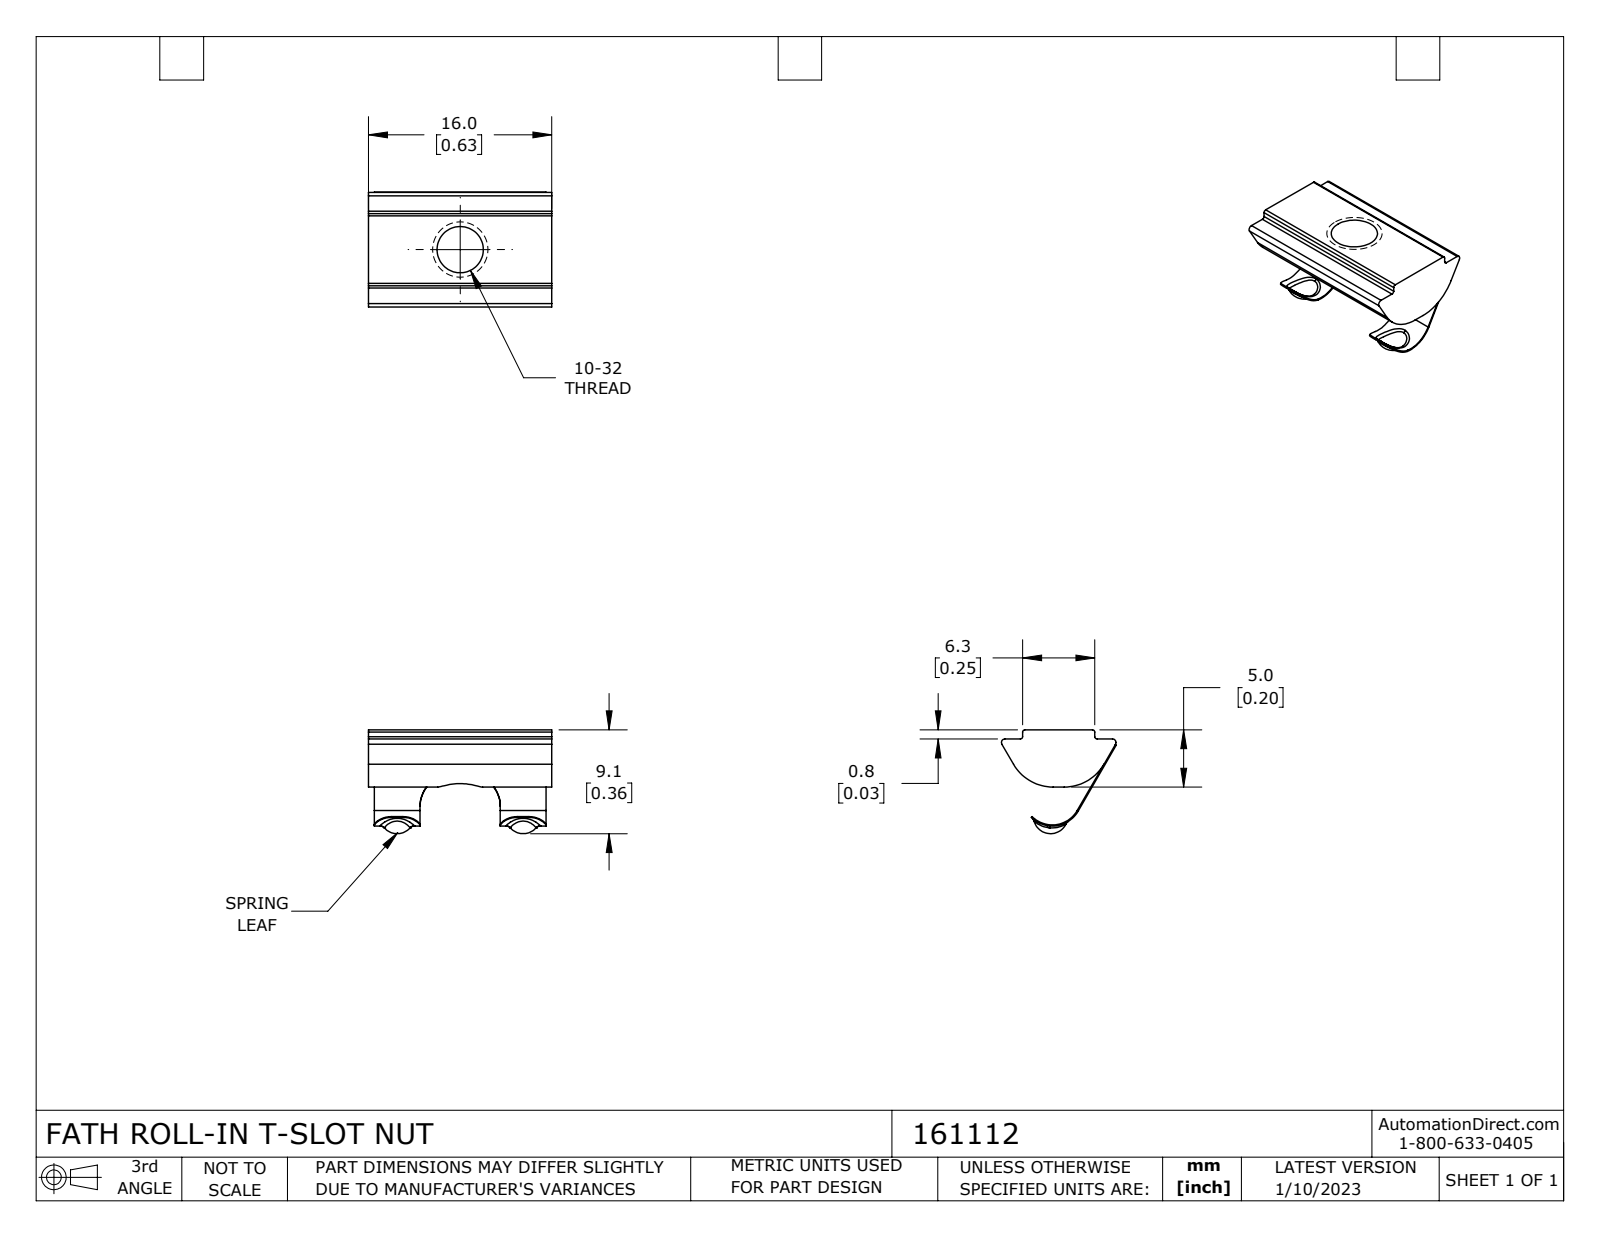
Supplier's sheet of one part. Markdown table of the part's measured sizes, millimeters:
| quantity | value |
| --- | --- |
| part name | 161112 |
| STEP written by | SolidWorks 2021 (CONFIG_CONTROL_DESIGN) |
| units | millimeters |
| bodies | 1 solid, 57 faces (20 planar, 21 cylindrical, 16 other) |
| overall size | 16 × 10 × 9.1 |
| volume | 540 mm³ |
| surface area | 695 mm² |
| round holes (diameter × count) | 4 × 1 |
| partial cylindrical surfaces (radius × count) | 0.2 × 4, 1.5 × 4, 0.3 × 2, 4 × 2, 2.5 × 1, 2.6 × 1, 3.5 × 1 |
| main face-to-face distances | 0.8, 16, 4.2, 5, 6.3, 0.5, 15.5, 15, 4.5, 11.5 |
